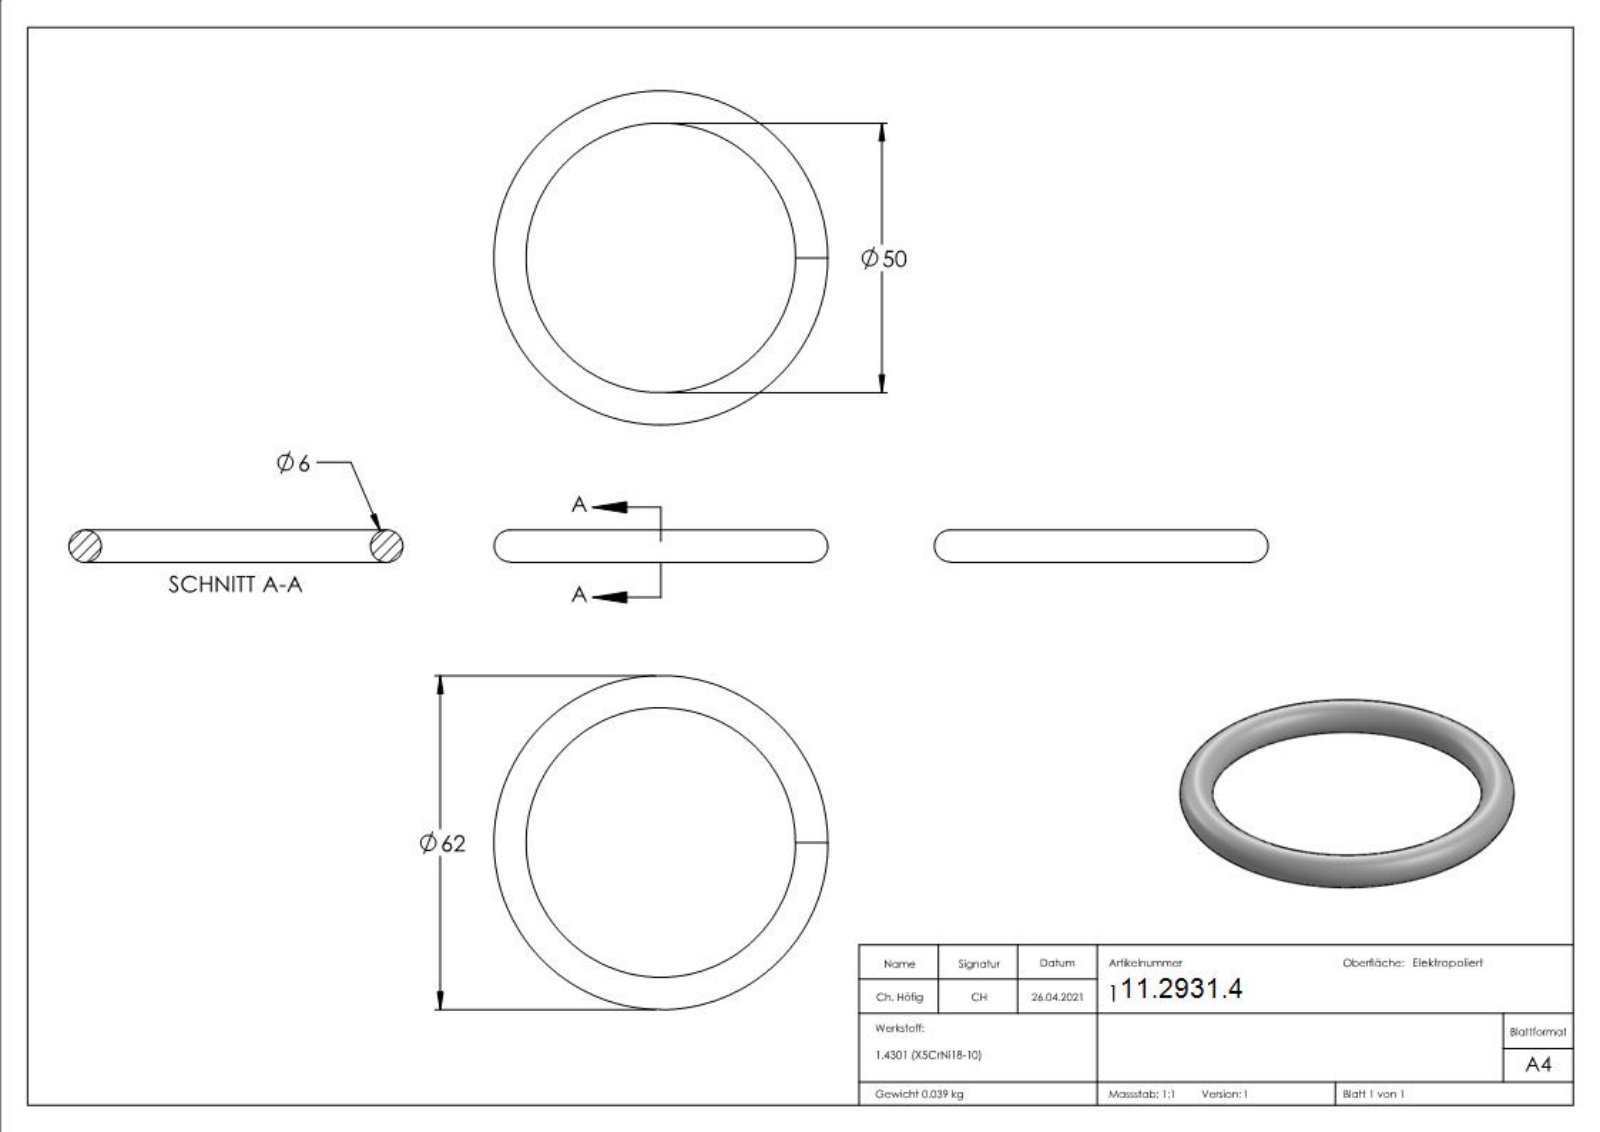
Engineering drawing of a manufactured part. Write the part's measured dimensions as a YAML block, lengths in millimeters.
part_name: "100053005"
step_written_by: "SolidWorks 2018 (CONFIG_CONTROL_DESIGN)"
units: millimeters
bodies: {solids: 1, faces: 4, planar: 0, cylindrical: 0, other: 4}
overall_size: [62, 62, 6]
volume: 4974
surface_area: 3316
